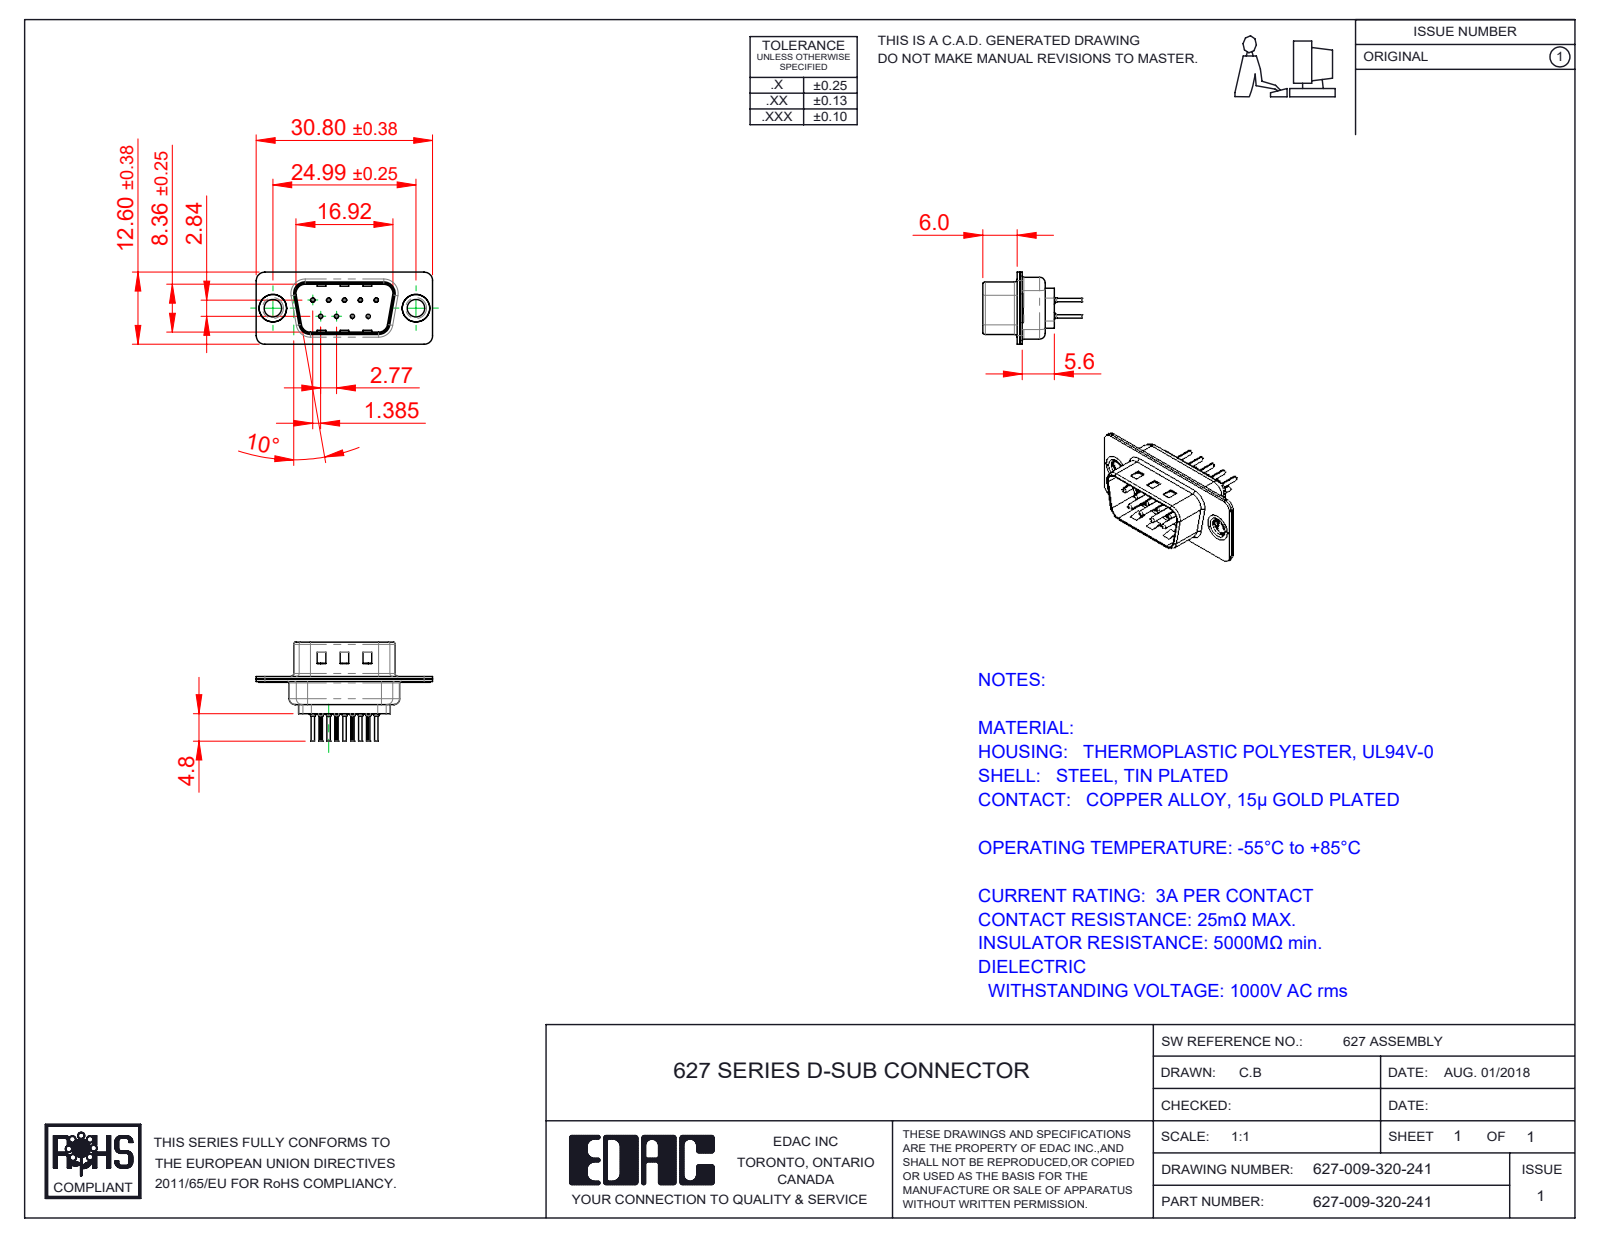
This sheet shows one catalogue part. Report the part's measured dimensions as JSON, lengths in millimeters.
{"part_name": "627 Shell Rear_09 Contacts; 627 Shell Front_09 Contacts; 627-009-320-241; 627 Thru Hole Rivet (+3 more)", "step_written_by": "SolidWorks 2020 (CONFIG_CONTROL_DESIGN)", "units": "millimeters", "bodies": {"solids": 14, "faces": 1160, "planar": 323, "cylindrical": 446, "other": 391}, "overall_size": [30.8, 17.3, 12.6], "volume_mm3": 1234, "surface_area_mm2": 3789, "round_holes": [[0.2, 9], [0.35, 9], [1.1, 9], [1.6, 9], [3.05, 2], [4, 2], [4.8, 2]], "round_bosses_or_shafts": [[2, 9], [1.5, 9], [0.75, 9], [0.6, 9], [5, 2], [4.9, 2], [3.55, 2]], "partial_cylinders_radius": [[0.1, 18], [1.5, 18], [2, 12], [0.5, 8], [1.6, 8], [0.25, 4], [0.6, 4], [0.65, 4]], "face_to_face_distances": [0.45, 0.4, 0.9, 0.82, 9.58, 1.4, 0.5, 8.76, 1.5, 5.6], "hole_center_spacings": [3.16, 2.77, 5.54, 5.03, 5.04, 8.31, 7.48, 7.49]}
